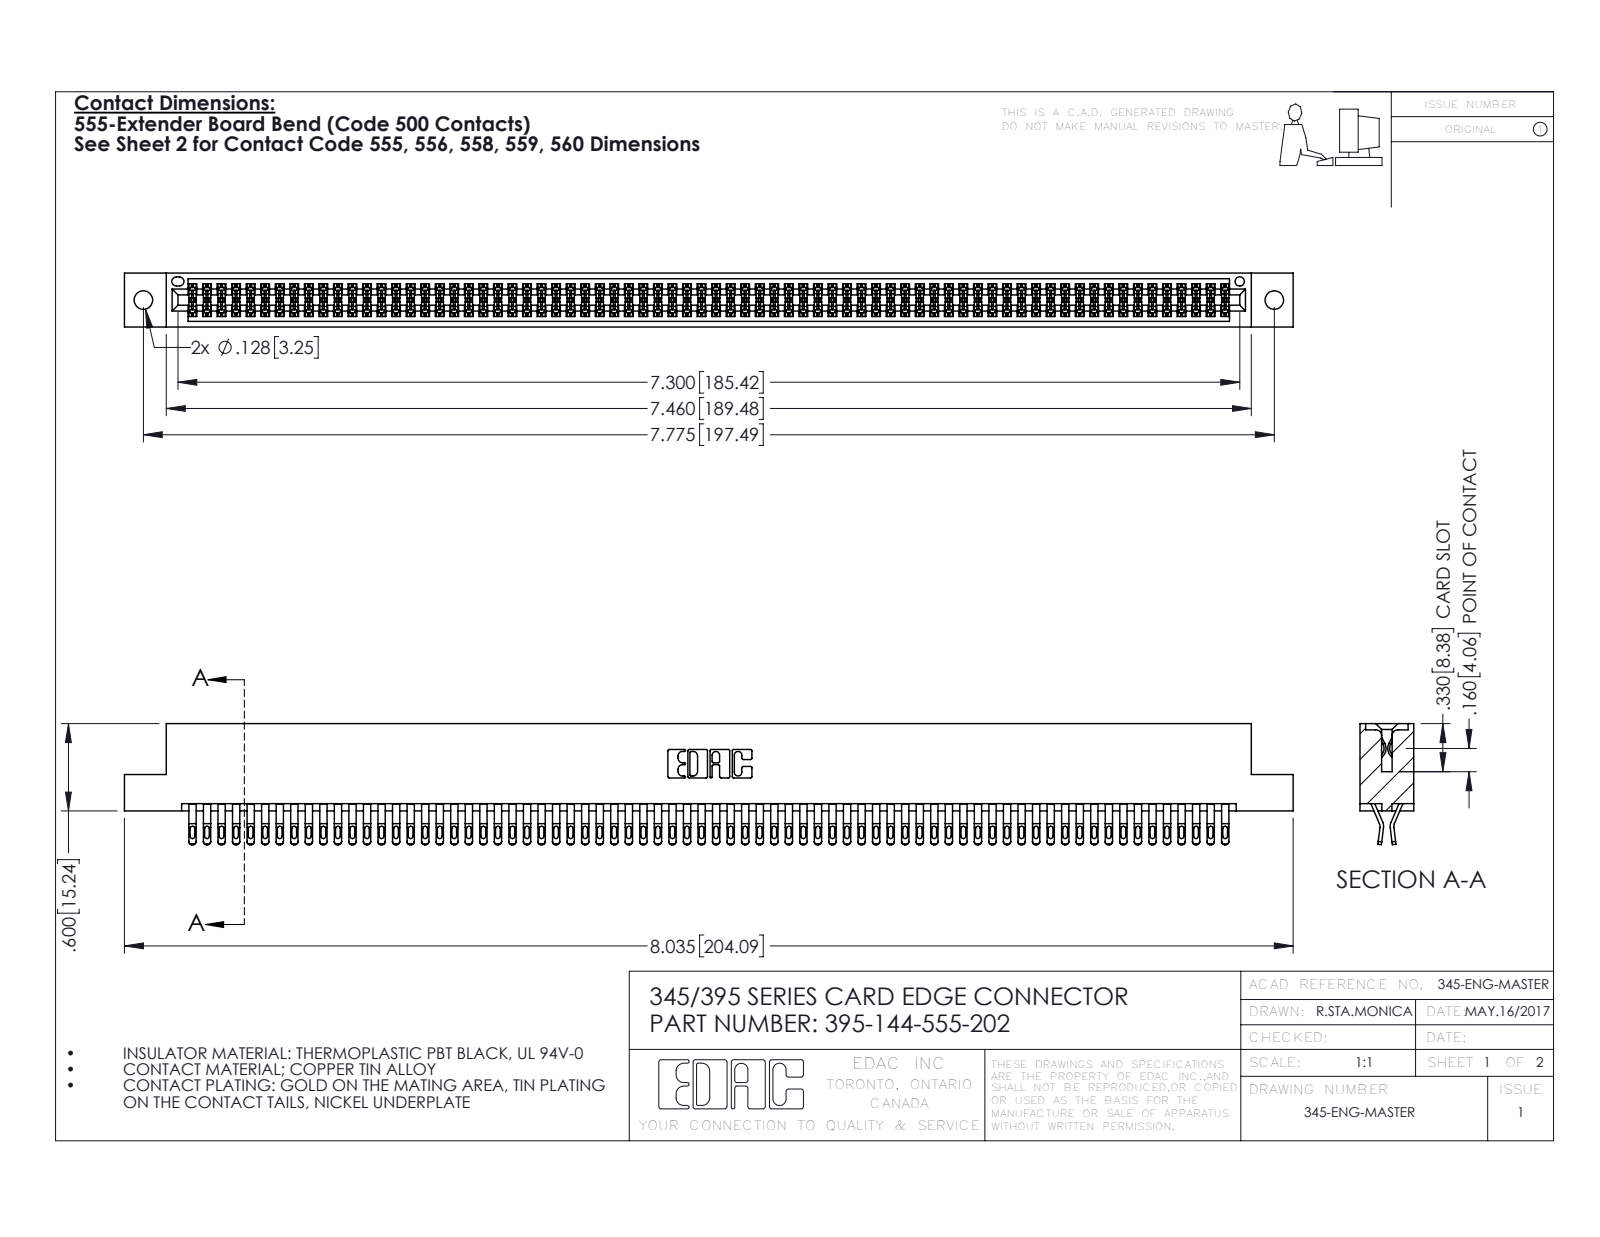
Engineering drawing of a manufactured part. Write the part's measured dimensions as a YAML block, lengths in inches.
part_name: "345 Part_Flush Mounting Lugs - 0.128 Dia; 395-144-555-202; 345-292-001_555 Tail"
step_written_by: "SolidWorks 2016 (CONFIG_CONTROL_DESIGN)"
units: inches
bodies: {solids: 145, faces: 8190, planar: 4544, cylindrical: 3646, other: 0}
overall_size: [8.035, 0.832, 0.37]
volume: 1.25
surface_area: 49.66
round_holes:
  - {diameter: 0.128, count: 2}
  - {diameter: 0.064, count: 1}
partial_cylinders:
  - {radius: 0.016, count: 360}
  - {radius: 0.02, count: 288}
  - {radius: 0.006, count: 216}
  - {radius: 0.01, count: 22}
  - {radius: 0.007, count: 6}
  - {radius: 0.031, count: 6}
  - {radius: 0.026, count: 3}
  - {radius: 0.01, count: 2}
face_to_face_distances: [0.298, 0.072, 0.025, 0.37, 0.2, 0.098, 0.272, 0.225, 0.175, 0.149]
hole_center_spacings: [0.27, 7.539, 7.775]
